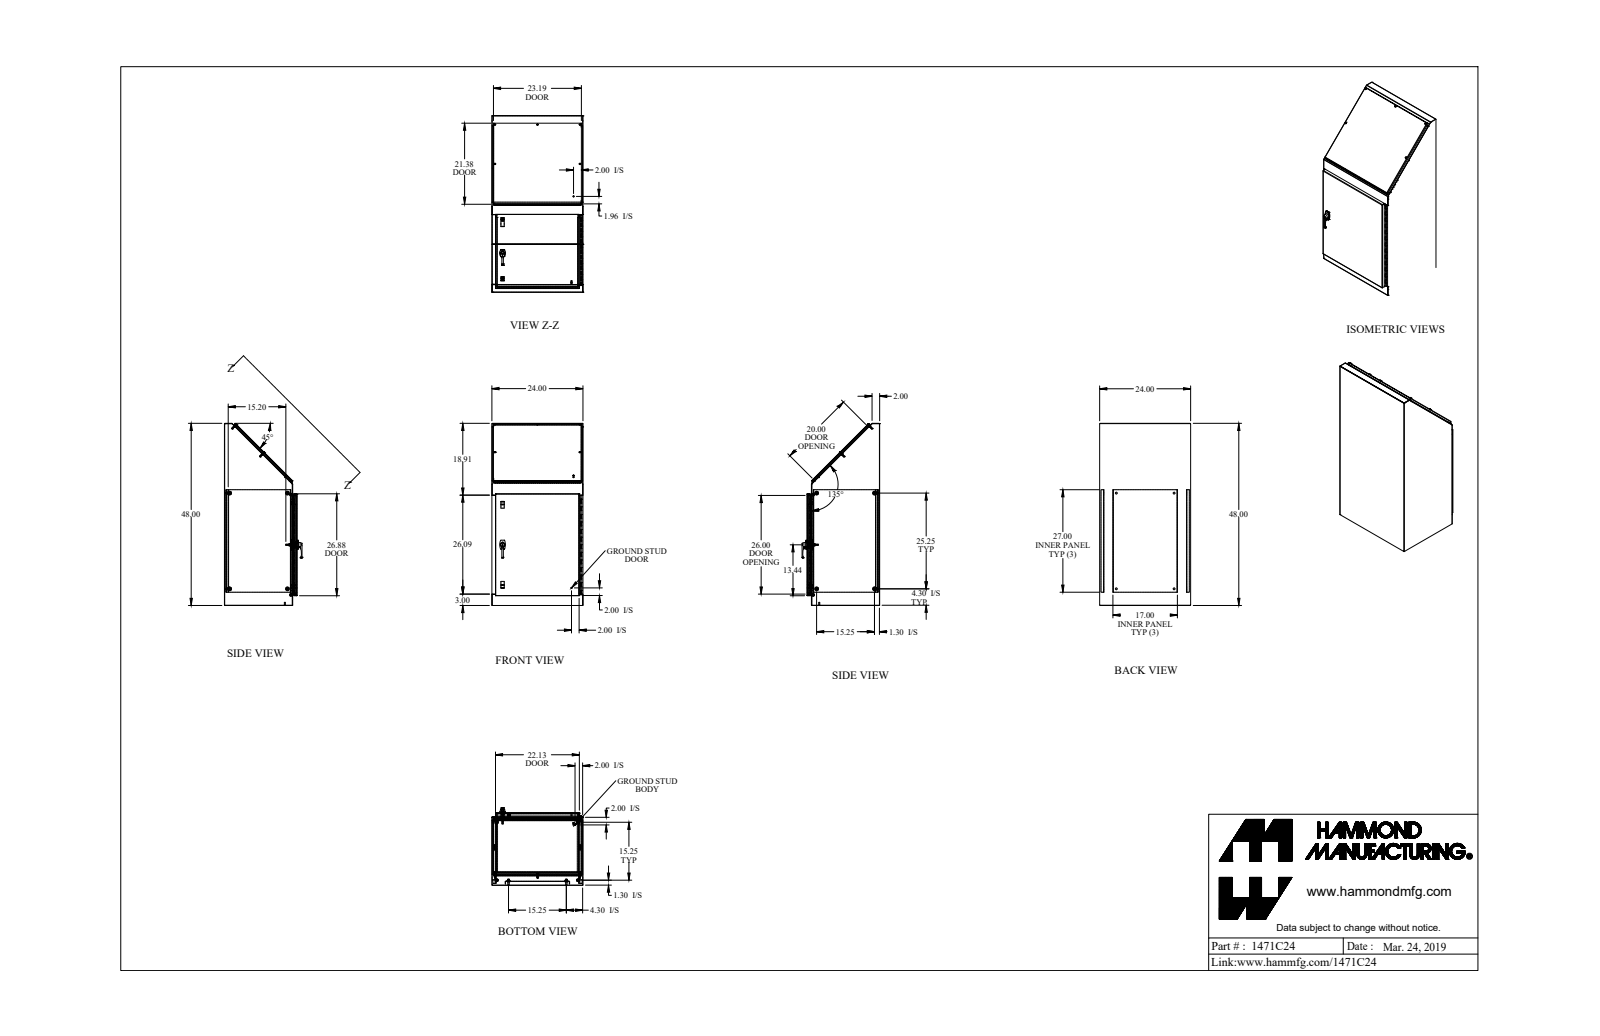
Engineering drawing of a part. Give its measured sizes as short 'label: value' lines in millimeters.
name: 1471C24_Default
written by: SolidWorks 2019 (CONFIG_CONTROL_DESIGN)
unit: mm
bodies: 107 solids, 2235 faces (1100 planar, 892 cylindrical, 243 other)
size: 1219.2 × 609.6 × 519.8
volume: 8 679 000 mm³; area: 8 551 000 mm²
holes: 12× ⌀12.7, 9× ⌀7.8, 6× ⌀6.4, 6× ⌀11.3, 5× ⌀4, 4× ⌀5.5, 3× ⌀4.7, 2× ⌀3.2, 2× ⌀4, 2× ⌀4.8, 2× ⌀5, 2× ⌀5
bosses: 11× ⌀25.4, 10× ⌀16.5, 10× ⌀8.4, 7× ⌀10.2, 7× ⌀9.5, 7× ⌀4.6, 5× ⌀12.7, 5× ⌀9.9
rounds: 23× R0.9, 23× R2.7, 15× R3.2, 8× R1.3, 8× R1.6, 6× R0.8, 6× R1.2, 6× R3.6
face distances: 1.8, 2.4, 607.8, 28, 26.2, 23.8, 25.6, 484.9, 581.6, 579.7
hole spacings: 749.2, 641.4, 387.4, 387.4, 641.4, 569.9, 387.4, 749.2
